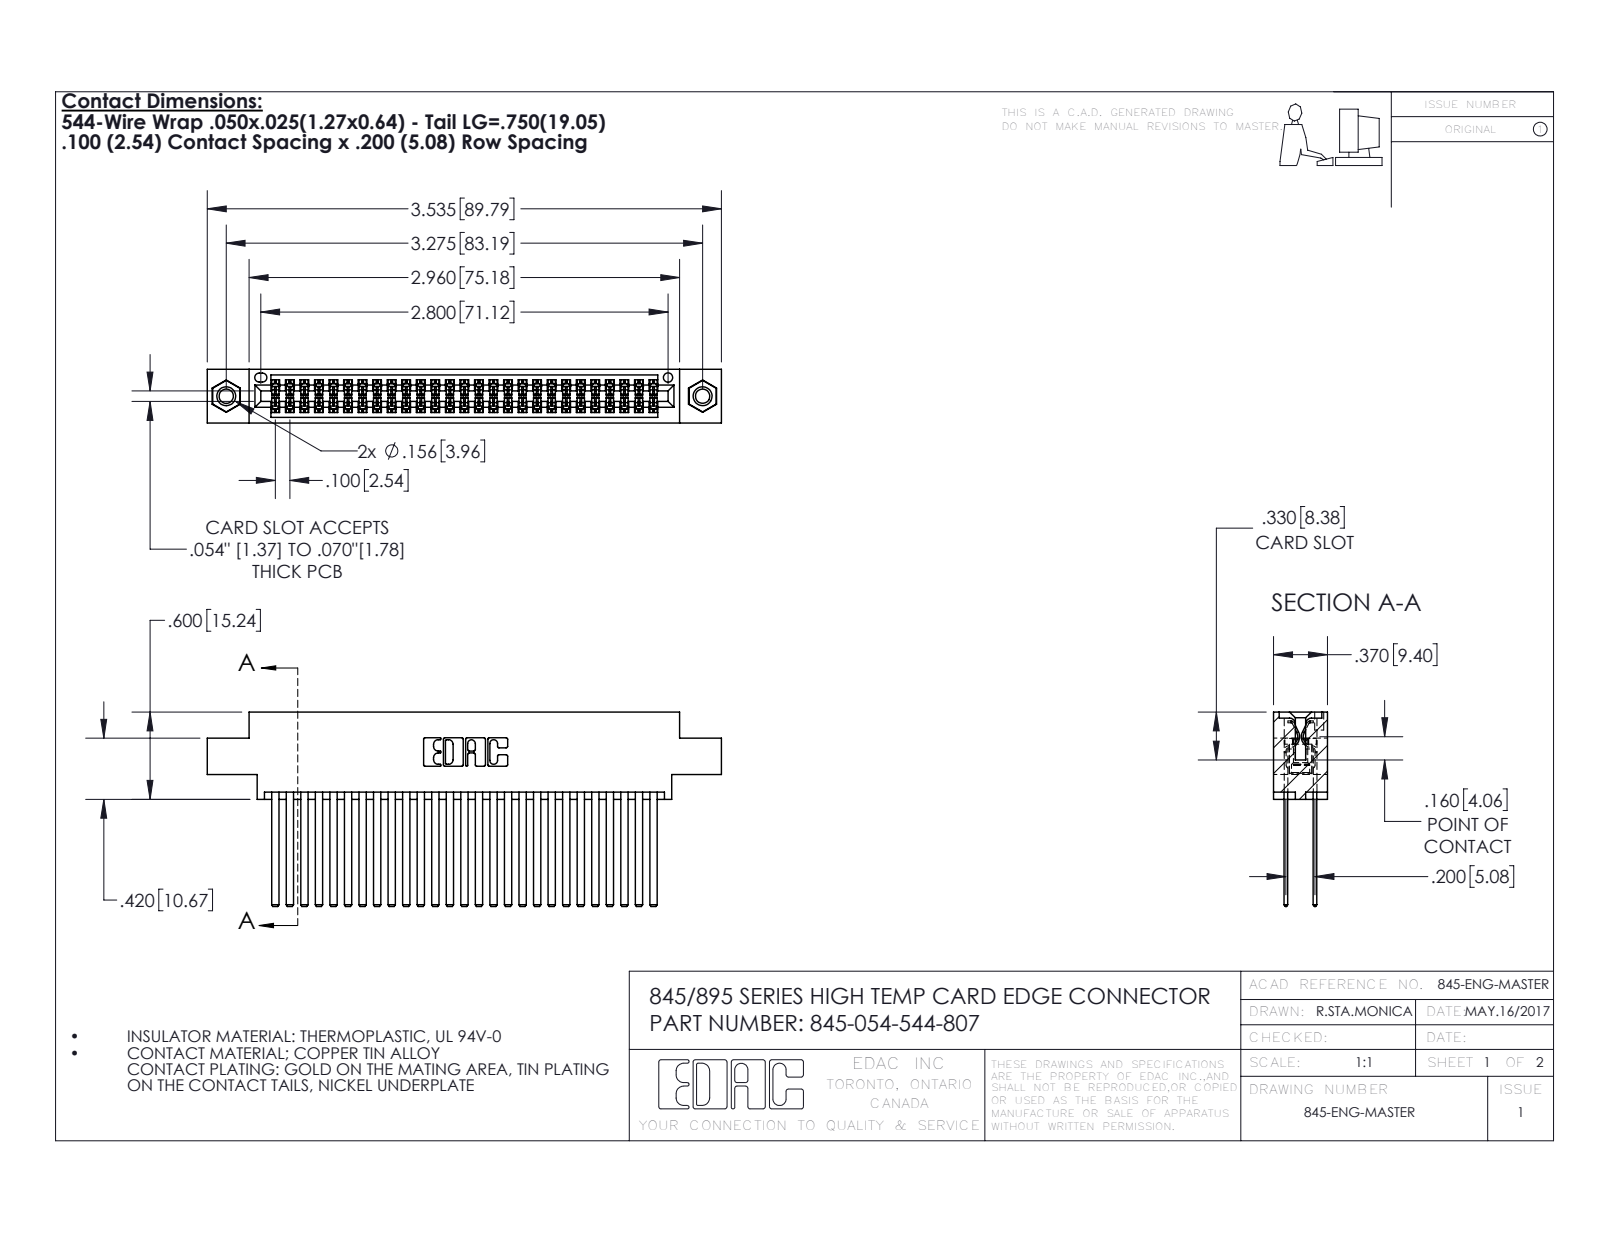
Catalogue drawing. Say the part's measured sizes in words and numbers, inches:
The part is named "345-054-544-807; 345 Part_0.170 Offset - 0.156 Dia-TI; 345-292-001_345-293-144; 345-250-001_345-250-005-103". Its 3-D file was written by "SolidWorks 2016 (CONFIG_CONTROL_DESIGN)". It is 33 solids with 1702 faces: 1154 planar, 532 cylindrical and 16 other. Overall it measures 3.535 by 1.337 by 0.37 inches. Its volume is 0.528 cubic inches and its surface area 19.67 square inches. Round holes: 2 of diameter 0.098, 2 of diameter 0.125, 2 of diameter 0.156, 1 of diameter 0.064. Round bosses or shafts: 2 of diameter 0.155. Partial cylindrical surfaces (rounded edges, fillets, slot ends): 57 of radius 0.006, 22 of radius 0.01, 6 of radius 0.007, 6 of radius 0.031, 3 of radius 0.026, 2 of radius 0.014, 2 of radius 0.019, 2 of radius 0.022. The main face-to-face distances are 0.072, 0.298, 0.098, 0.025, 0.272, 0.37, 0.2, 0.225, 0.175, 0.15. The hole center spacings are 0.27, 3.04, 3.275.
